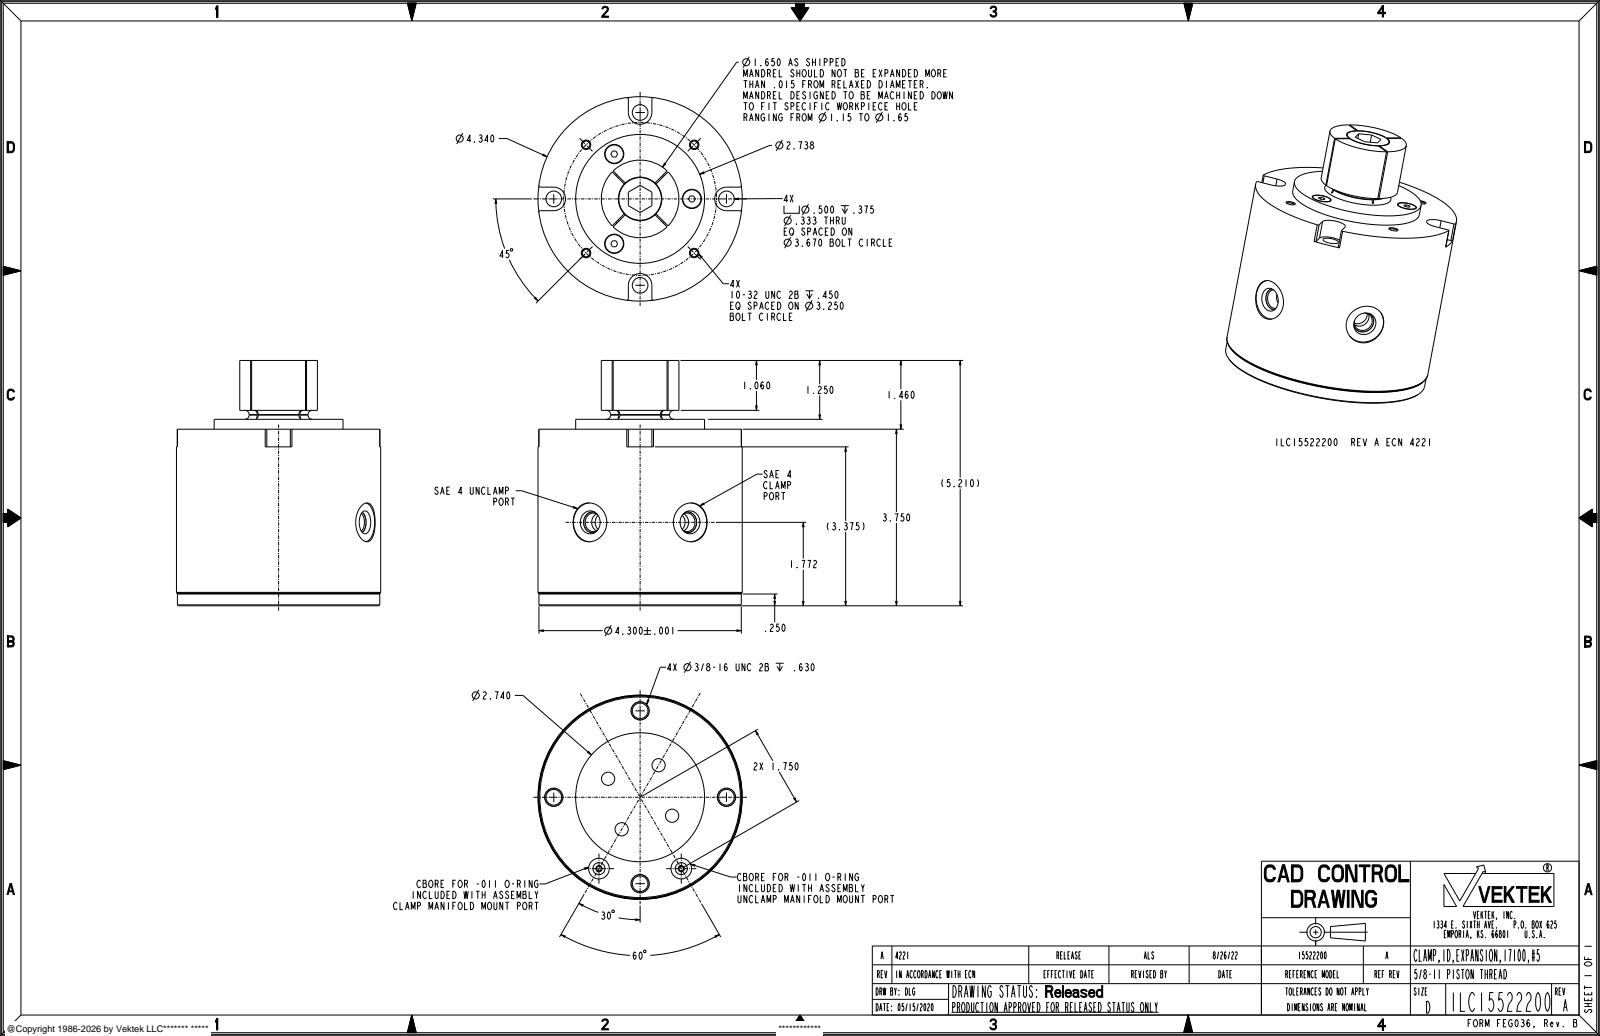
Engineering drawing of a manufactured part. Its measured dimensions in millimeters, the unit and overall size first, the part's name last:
Units: millimetres
Overall size (bounding box): 132.3 × 110.2 × 110.2
Round holes (diameter × count): ⌀4.1 ×4, ⌀7.1 ×4, ⌀8.5 ×4, ⌀10.4 ×3, ⌀2.5 ×2, ⌀6.5 ×2, ⌀10 ×2, ⌀11.1 ×2, ⌀21 ×2, ⌀23.5 ×1, ⌀69.6 ×1
Round bosses / shafts (diameter × count): ⌀9.5 ×4, ⌀4.8 ×4, ⌀9.9 ×3, ⌀11.1 ×2, ⌀3 ×2, ⌀110.2 ×1, ⌀109.2 ×1, ⌀69.5 ×1
Partial cylindrical surfaces — rounded edges, fillets, slot ends (radius × count): R0.8 ×8, R6.4 ×4
Main face-to-face distances: 95.3, 94.9, 0.4, 5.3, 100.2, 100.6, 31.8, 37.1, 132, 132.3
Hole centre spacings: 34, 81.2, 19.9, 22.6, 28.2, 31, 40.5, 40.9
Volume: 933 600 mm³ · Surface area: 76 840 mm²
Bodies: 1 solid, 268 faces (96 planar, 118 cylindrical, 54 other)
Part name (STEP PRODUCT): ILC15522200
STEP written by: CREO PARAMETRIC BY PTC INC, 2021164 (AUTOMOTIVE_DESIGN)
